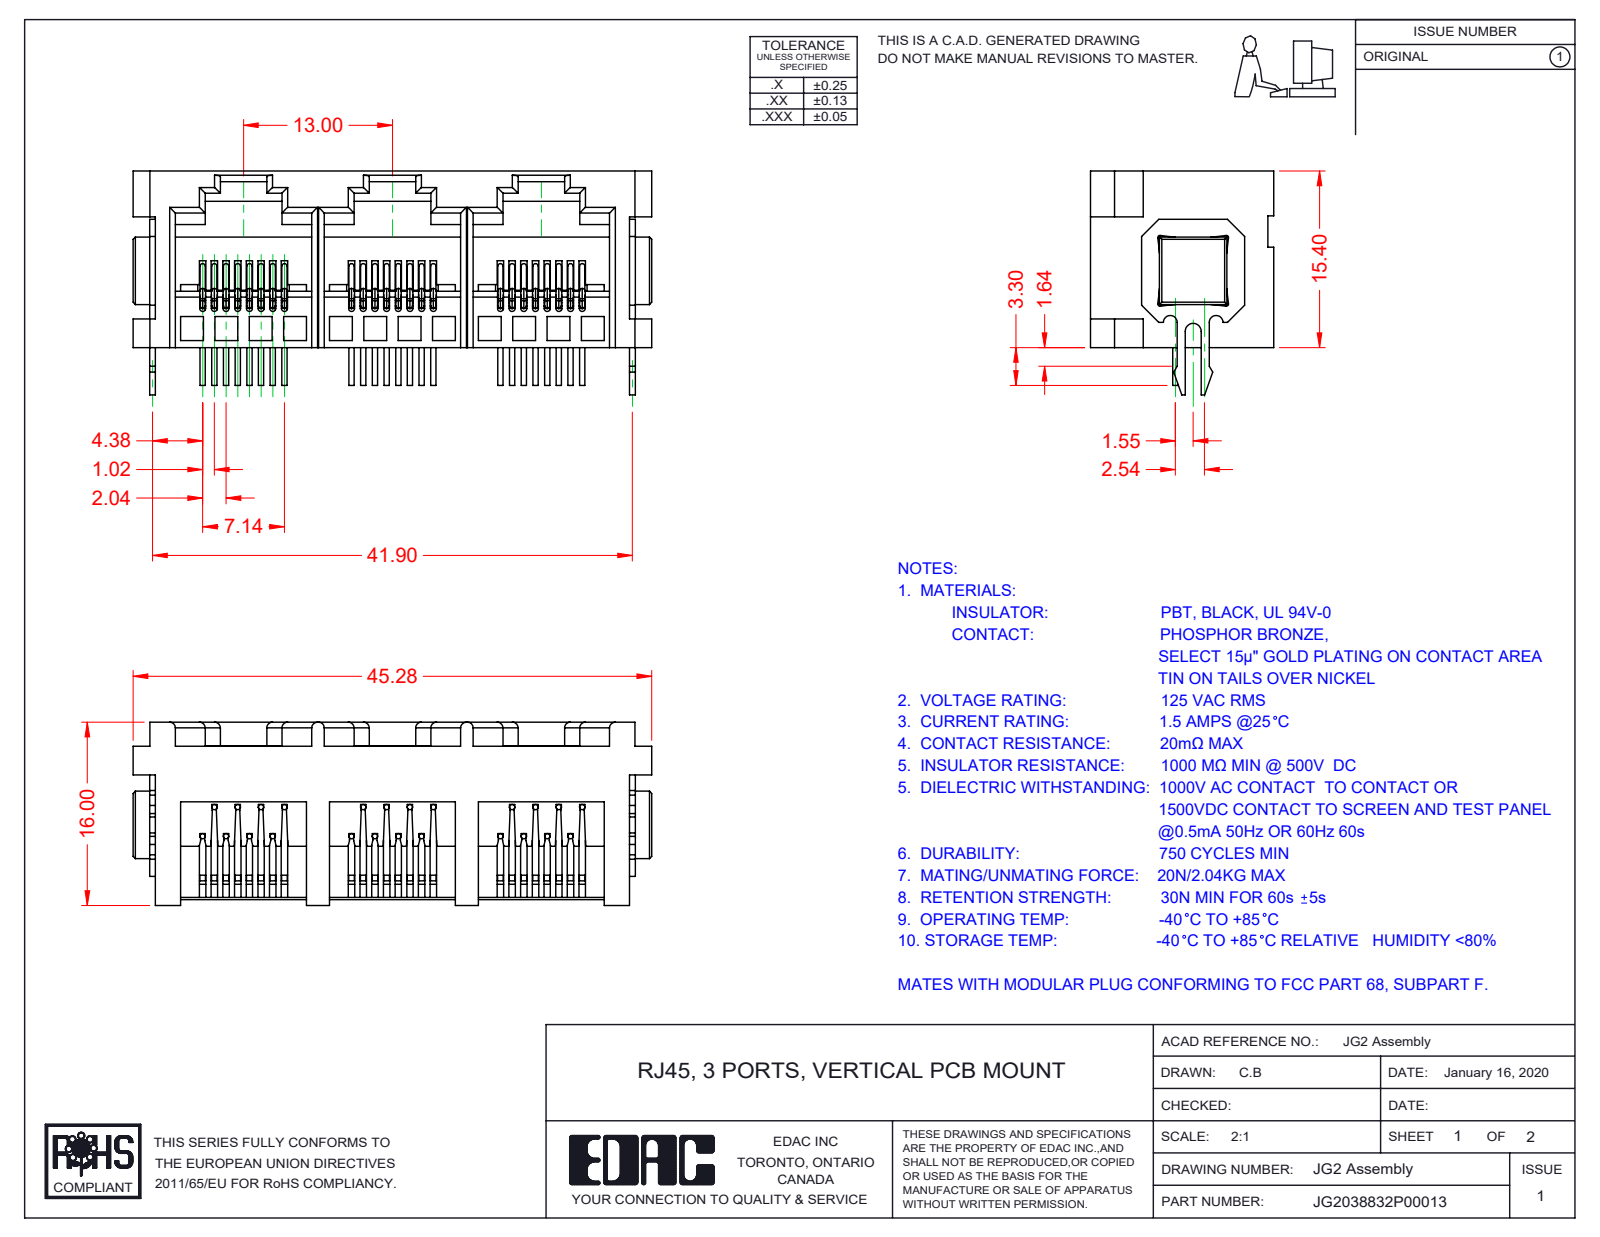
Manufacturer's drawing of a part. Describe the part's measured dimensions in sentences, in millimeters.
The part is named "G2 Boardlock2; G2 Contacts; G2 Contact Lock; G2 Insulator (+2 more)". Its 3-D file was written by "SolidWorks 2016 (CONFIG_CONTROL_DESIGN)". It is 30 solids with 1835 faces: 1210 planar, 457 cylindrical and 168 other. Overall it measures 45.28 by 19.54 by 16 millimeters. Its volume is 4 876 cubic millimeters and its surface area 9 571 square millimeters. Round bosses or shafts: 96 of diameter 0.46. Partial cylindrical surfaces (rounded edges, fillets, slot ends): 69 of radius 0.5, 4 of radius 0.2, 4 of radius 20.35, 3 of radius 0.3, 2 of radius 0.6, 1 of radius 0.21, 1 of radius 0.45, 1 of radius 0.7. The main face-to-face distances are 13, 12, 0.5, 3.4, 2.2, 11.08, 0.92, 26, 11, 2.
